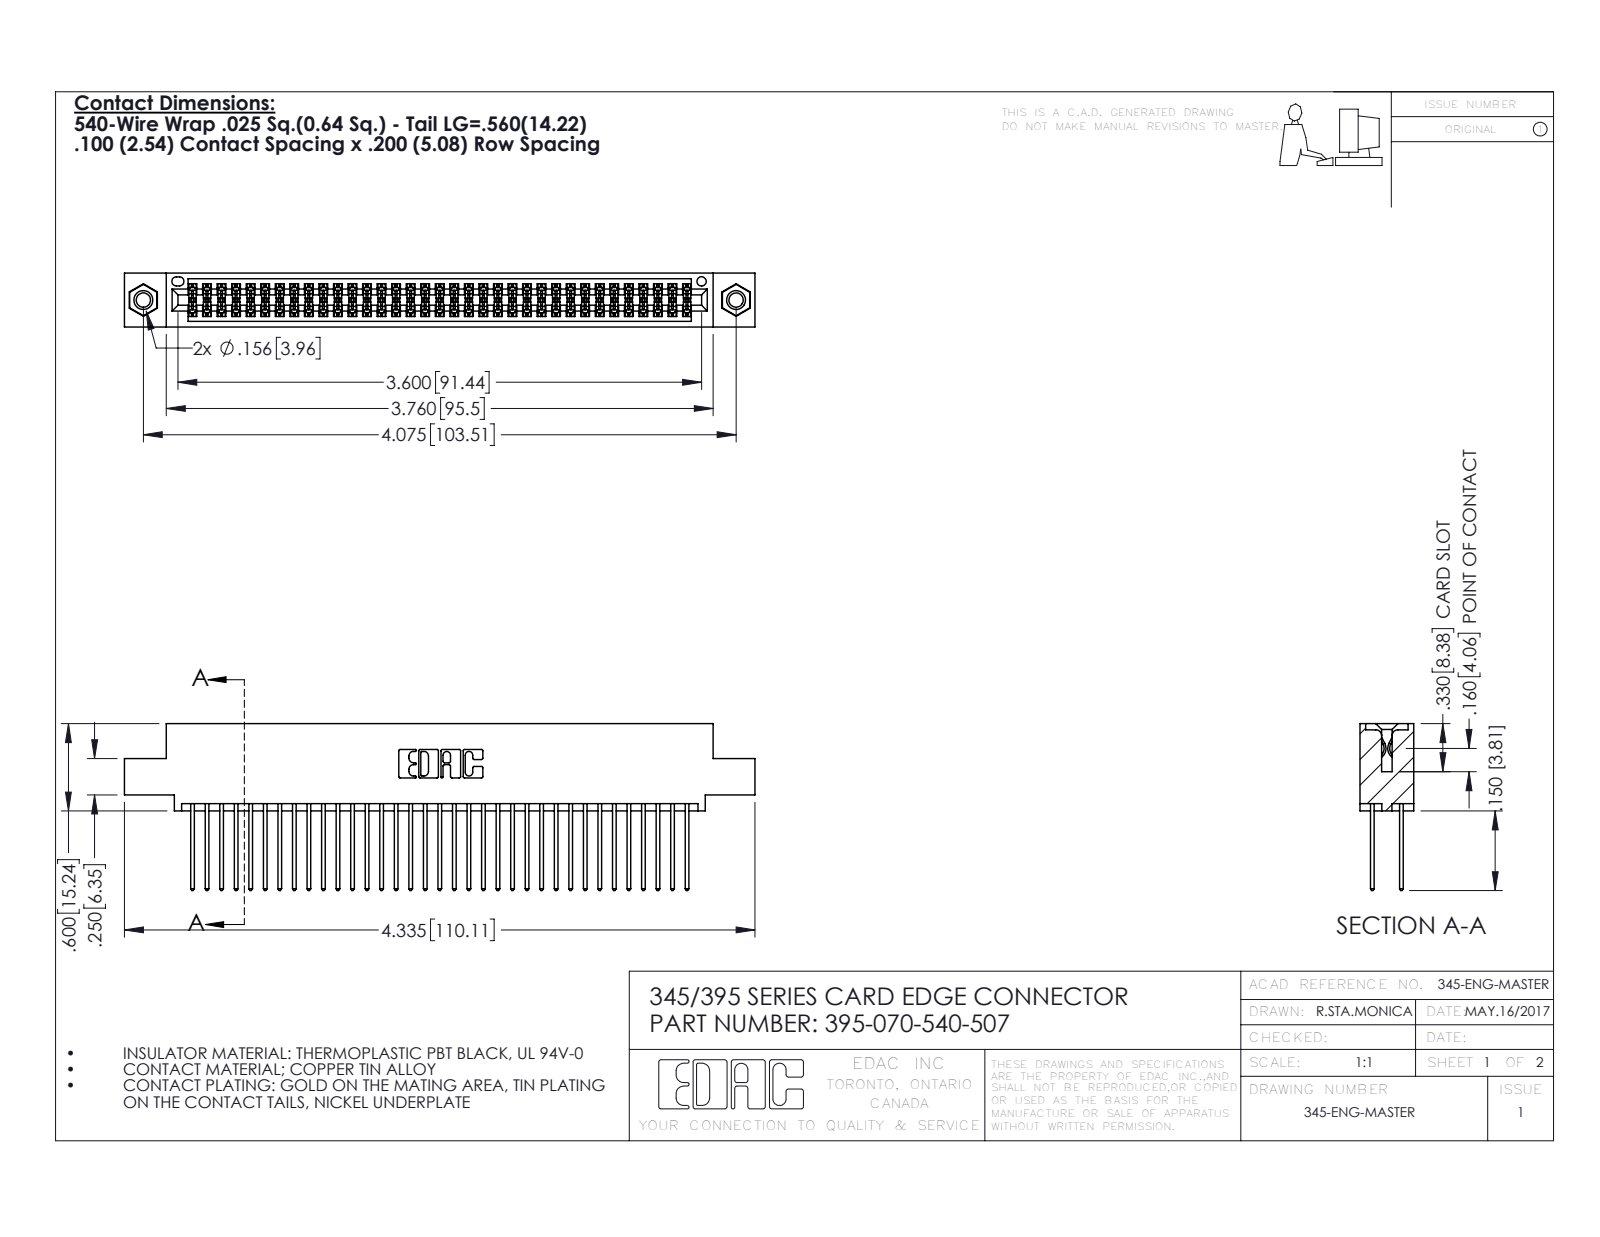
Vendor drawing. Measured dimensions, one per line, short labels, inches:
name: 395-070-540-507; 345 Part_0.110 Offset - 0.156 Dia-TI; 345-292-001_345-293-140; 345-250-001_345-250-005-103
written by: SolidWorks 2016 (CONFIG_CONTROL_DESIGN)
unit: in
bodies: 73 solids, 3690 faces (2426 planar, 1248 cylindrical, 16 other)
size: 4.335 × 1.147 × 0.37
volume: 0.66 in³; area: 26.65 in²
holes: 2× ⌀0.098, 2× ⌀0.125, 2× ⌀0.156, 1× ⌀0.064
bosses: 2× ⌀0.155
rounds: 105× R0.006, 70× R0.01, 22× R0.01, 6× R0.007, 6× R0.031, 3× R0.026, 2× R0.014, 2× R0.019
face distances: 0.072, 0.298, 0.2, 0.098, 0.272, 0.025, 0.37, 0.225, 0.175, 0.149
hole spacings: 0.27, 3.839, 4.075
